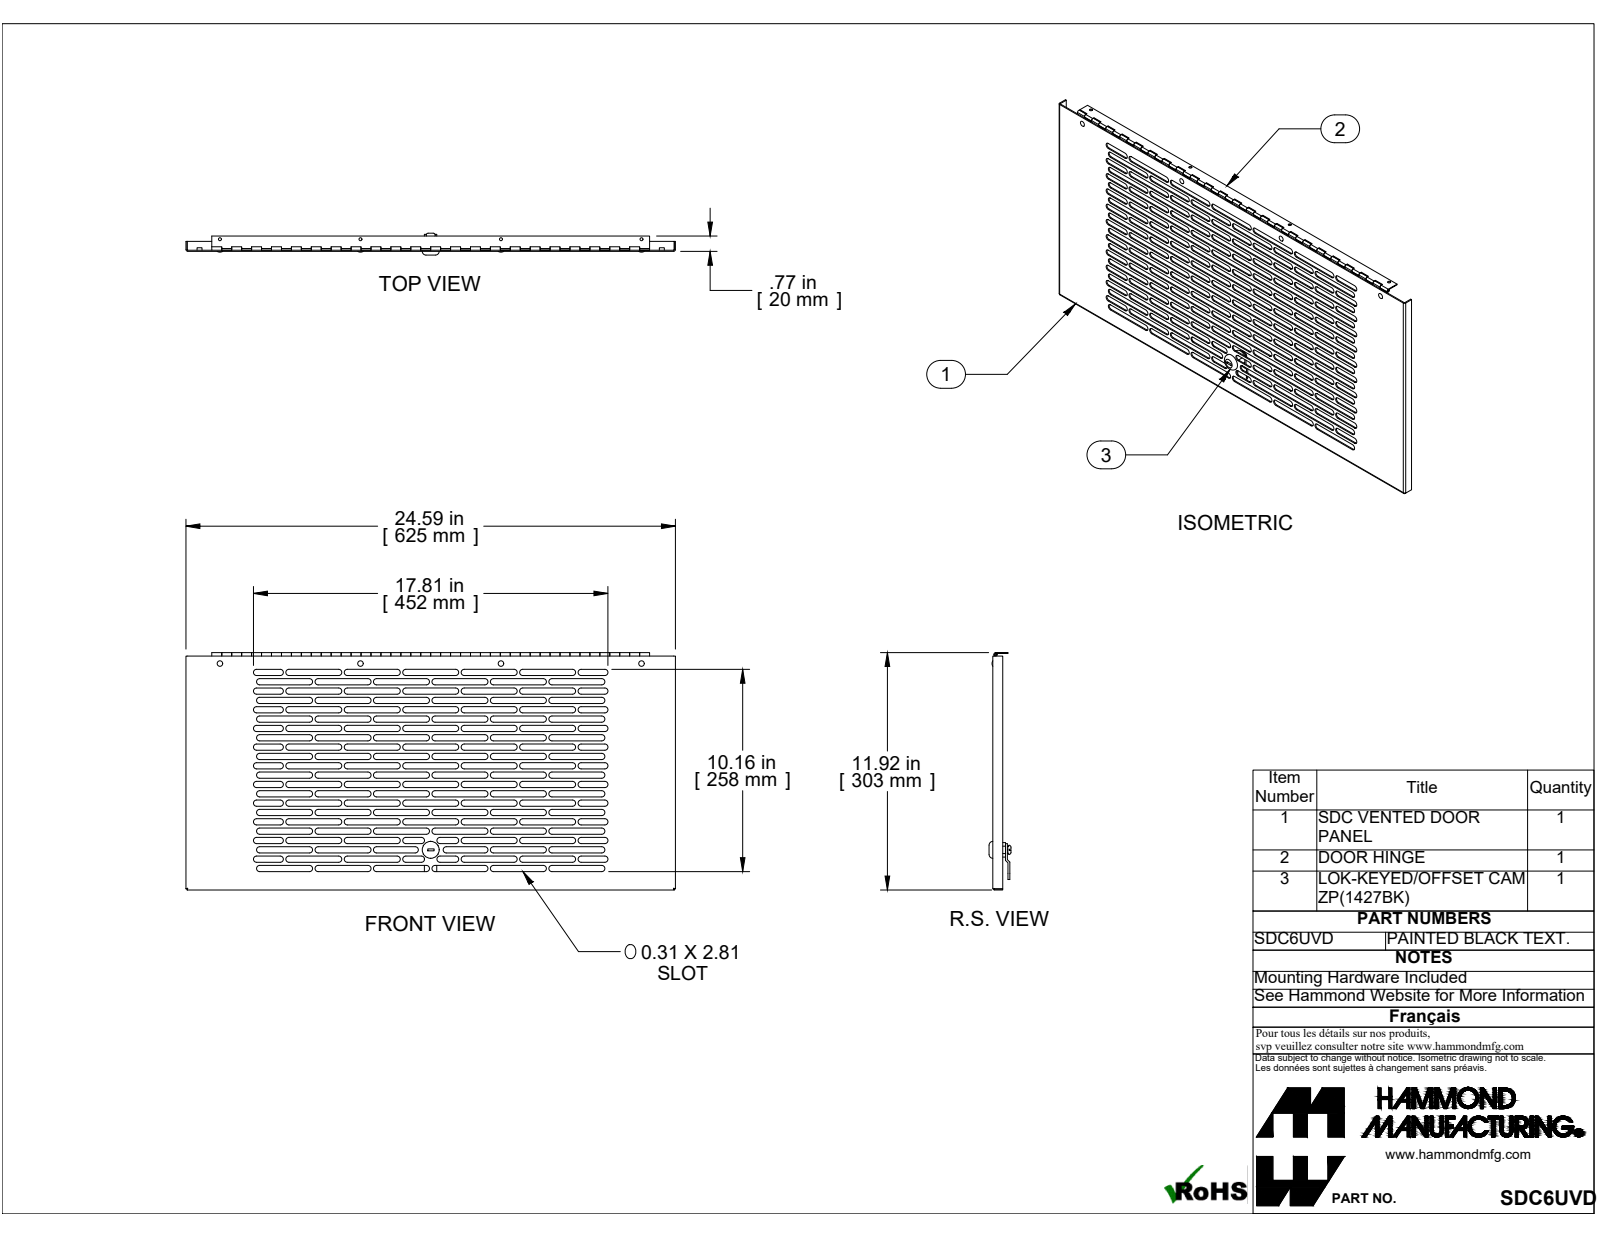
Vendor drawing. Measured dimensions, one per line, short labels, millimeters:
name: SDC6UVD
written by: SolidWorks 2019 (CONFIG_CONTROL_DESIGN)
unit: mm
bodies: 14 solids, 993 faces (568 planar, 409 cylindrical, 16 other)
size: 624.7 × 302.9 × 27.9
volume: 217 300 mm³; area: 340 500 mm²
holes: 8× ⌀3.8, 4× ⌀3.2, 1× ⌀2.3, 1× ⌀5.2, 1× ⌀15.2
bosses: 1× ⌀18.5, 1× ⌀5.9, 1× ⌀4.4, 1× ⌀2
rounds: 234× R4, 44× R4, 12× R4, 3× R0.7, 3× R2.2, 2× R7.9, 1× R9.7
face distances: 1.4, 1, 1.4, 2.5, 301.8, 302.9, 300.4, 301.4, 623.2, 47.7
hole spacings: 179.4, 358.8, 179.4, 254, 359, 538.1
